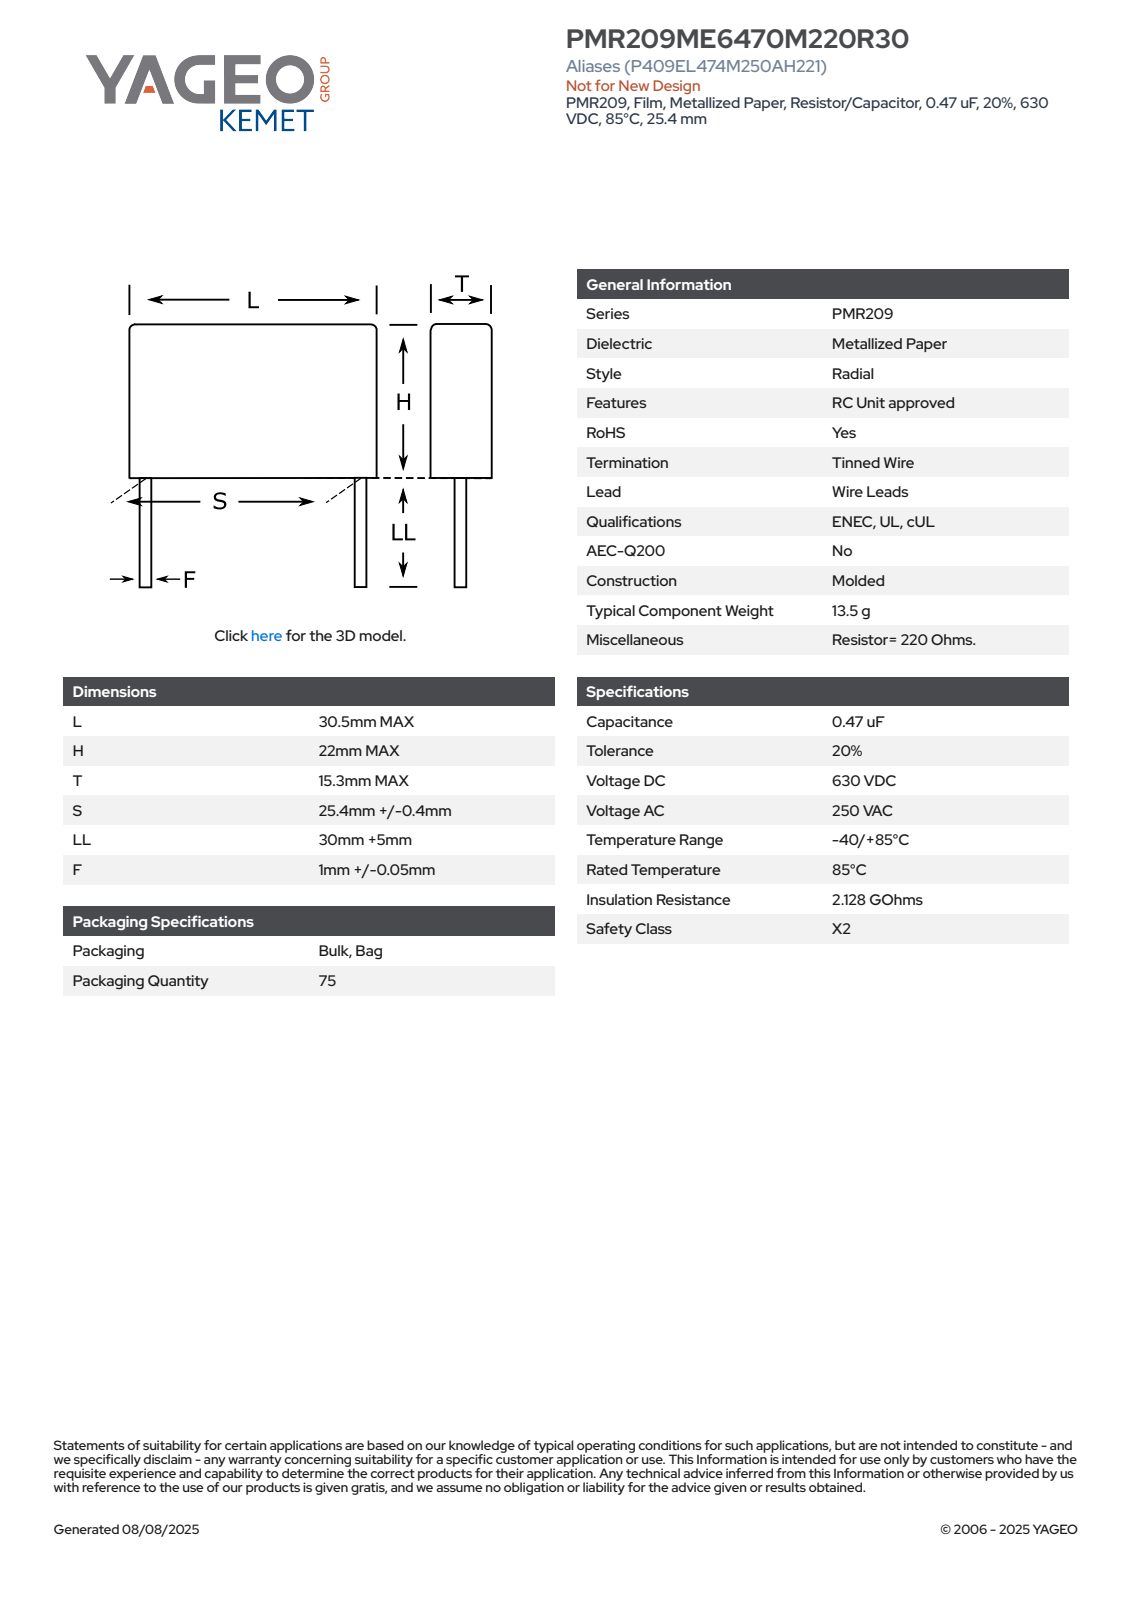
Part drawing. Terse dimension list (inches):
name: CFR_MOLDED_30.5X22X15.3_L30.5H22T15.3S25.4LL35F1.05
written by: SolidWorks 2014 (AUTOMOTIVE_DESIGN)
unit: in
bodies: 4 solids, 73 faces (65 planar, 8 cylindrical, 0 other)
size: 2.244 × 1.201 × 0.602
volume: 0.63 in³; area: 4.966 in²
bosses: 2× ⌀0.041
rounds: 4× R0.02
face distances: 0.602, 0.866, 1.201, 0.603, 1.378, 2.244, 1.849, 0.471, 0.395, 1.741
